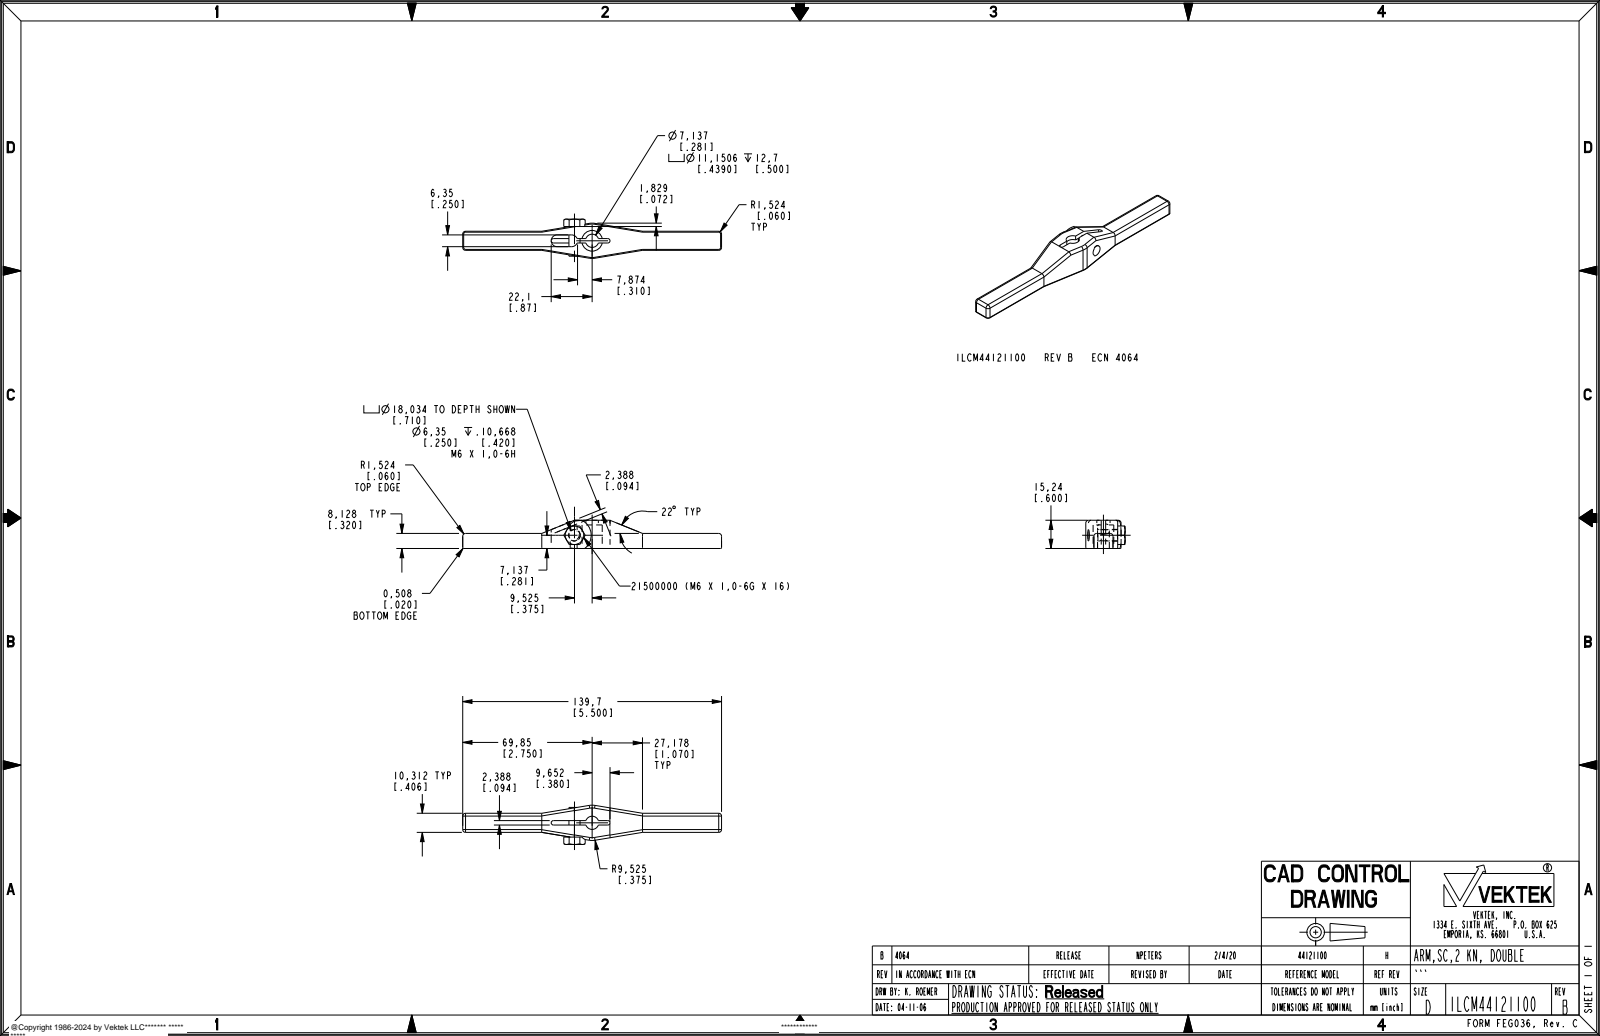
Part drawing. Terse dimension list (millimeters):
name: ILCM44121100
written by: PRO/ENGINEER BY PARAMETRIC TECHNOLOGY CORPORATION, 2013320 (AUTOMOTIVE_DESIGN)
unit: mm
bodies: 1 solid, 108 faces (40 planar, 50 cylindrical, 18 other)
size: 139.7 × 21.21 × 15.24
volume: 15 512 mm³; area: 7 458 mm²
holes: 1× ⌀6.35, 1× ⌀11.15
bosses: 1× ⌀5.99
rounds: 16× R1.52, 8× R0.51, 2× R1.19, 2× R3.17, 1× R2.51, 1× R3.57, 1× R9.02, 1× R9.53
face distances: 8.13, 10.32, 19.06, 3.97, 6.35, 15.24, 7.11, 2.38, 1.99, 8.33
